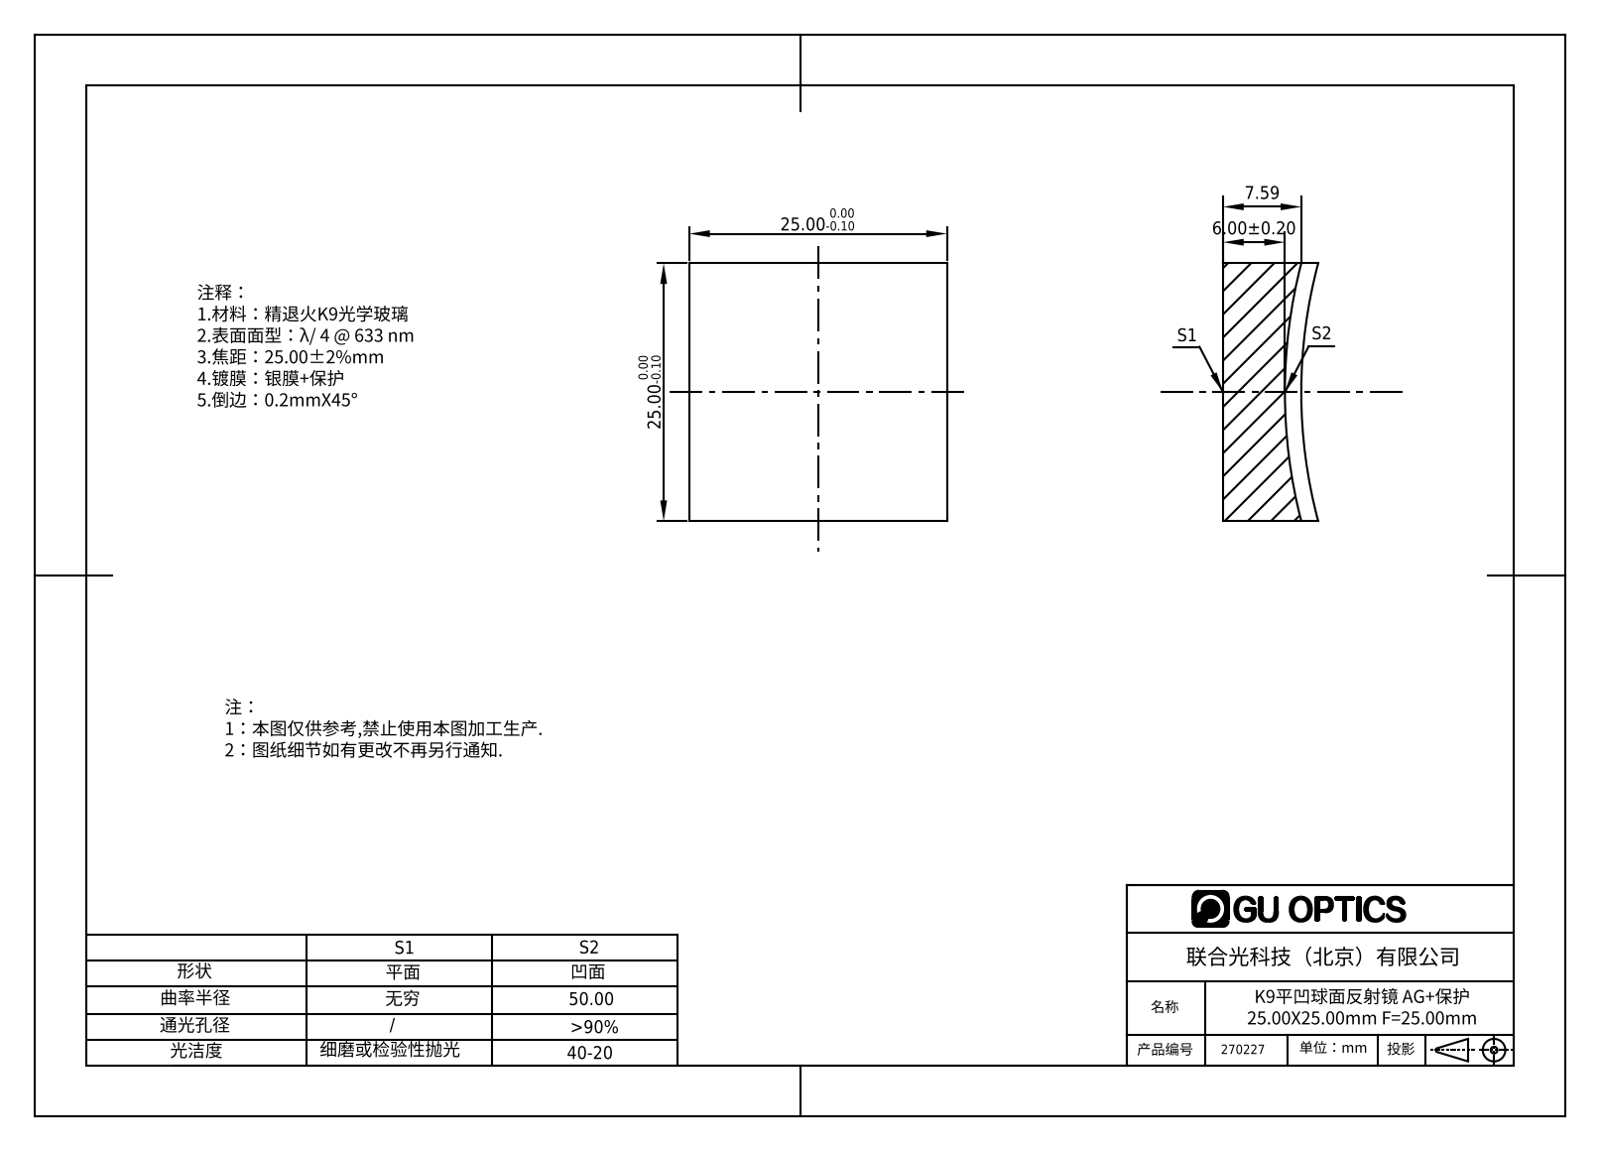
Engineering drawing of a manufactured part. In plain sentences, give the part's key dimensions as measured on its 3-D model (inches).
The part is named "270032". Its 3-D file was written by "SolidWorks 2019 (AUTOMOTIVE_DESIGN)". It is 1 solid with 7 faces: 5 planar, 0 cylindrical and 2 other. Overall it measures 0.984 by 0.984 by 0.363 inches. Its volume is 0.269 cubic inches and its surface area 3.219 square inches. The main face-to-face distances are 0.984.
